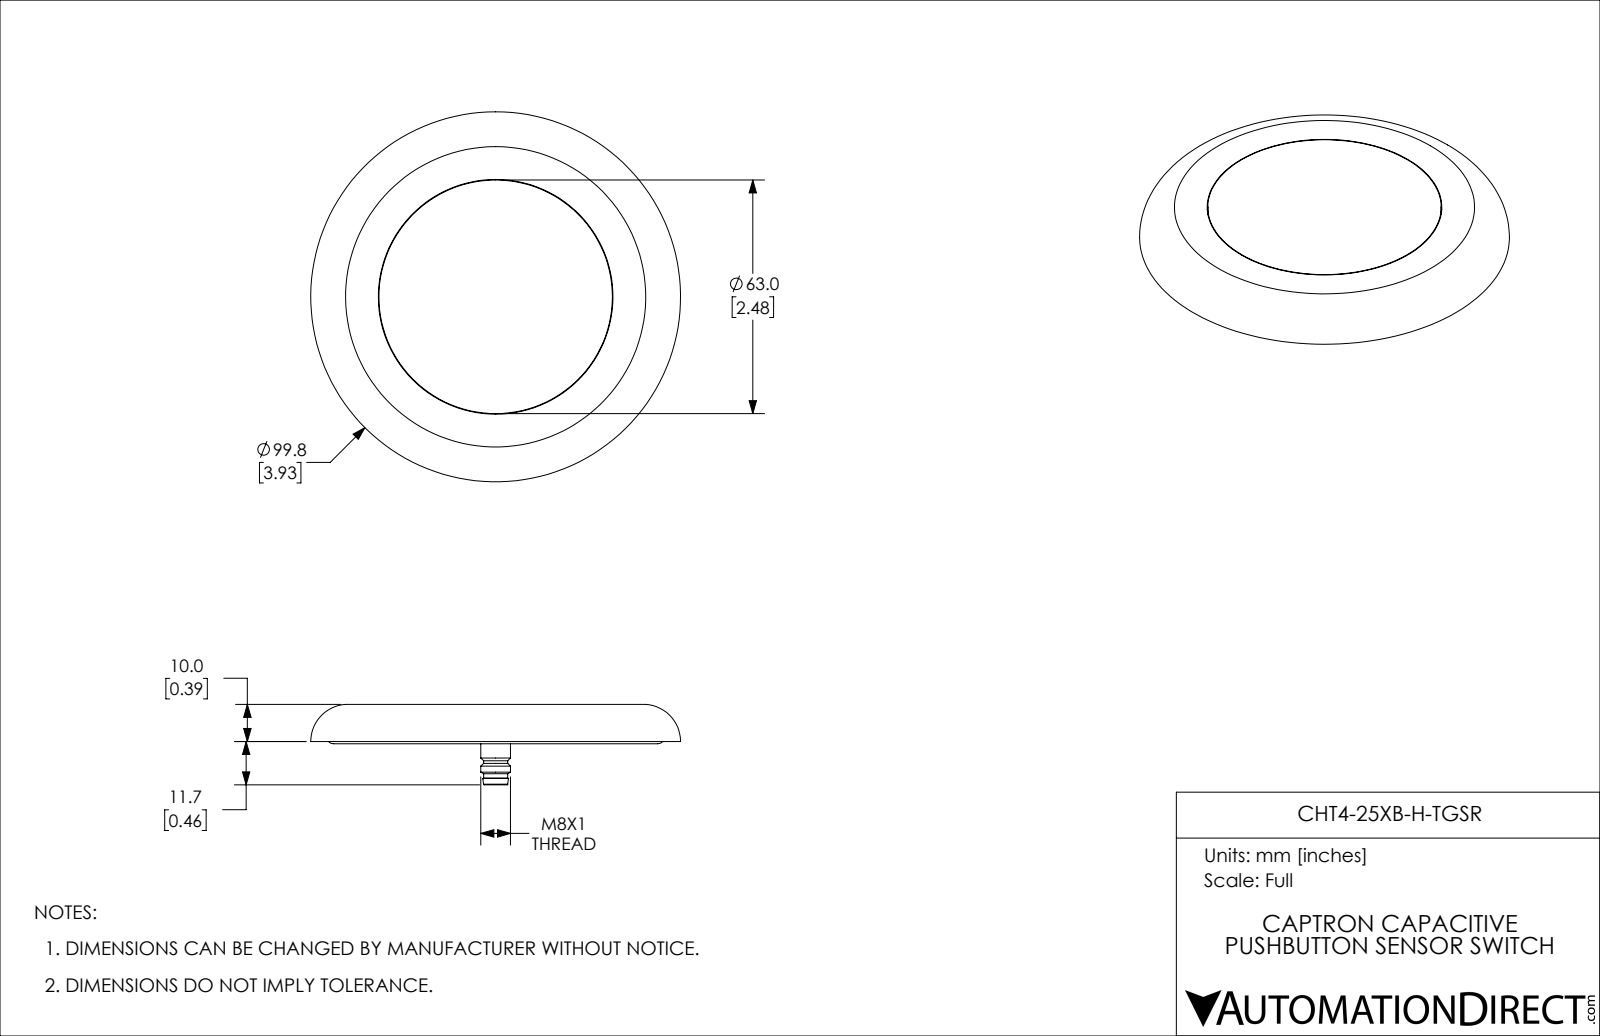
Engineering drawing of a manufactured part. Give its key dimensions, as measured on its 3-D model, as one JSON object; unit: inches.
{"part_name": "CHT4-25XB-H-TGSR", "step_written_by": "SolidWorks 2019 (CONFIG_CONTROL_DESIGN)", "units": "inches", "bodies": {"solids": 9, "faces": 106, "planar": 25, "cylindrical": 35, "other": 46}, "overall_size": [3.929, 3.929, 0.854], "volume_in3": 1.761, "surface_area_in2": 64, "round_holes": [[0.228, 1], [2.299, 1], [2.493, 1], [2.543, 1]], "round_bosses_or_shafts": [[0.039, 5], [2.48, 1], [0.315, 1], [0.256, 1]], "partial_cylinders_radius": [[0.02, 2], [0.039, 1], [1.26, 1]], "face_to_face_distances": [0.326, 0.056, 0.382, 0.057, 0.324, 0.269, 0.057, 0.064, 0.332, 0.39], "hole_center_spacings": [0.126]}
